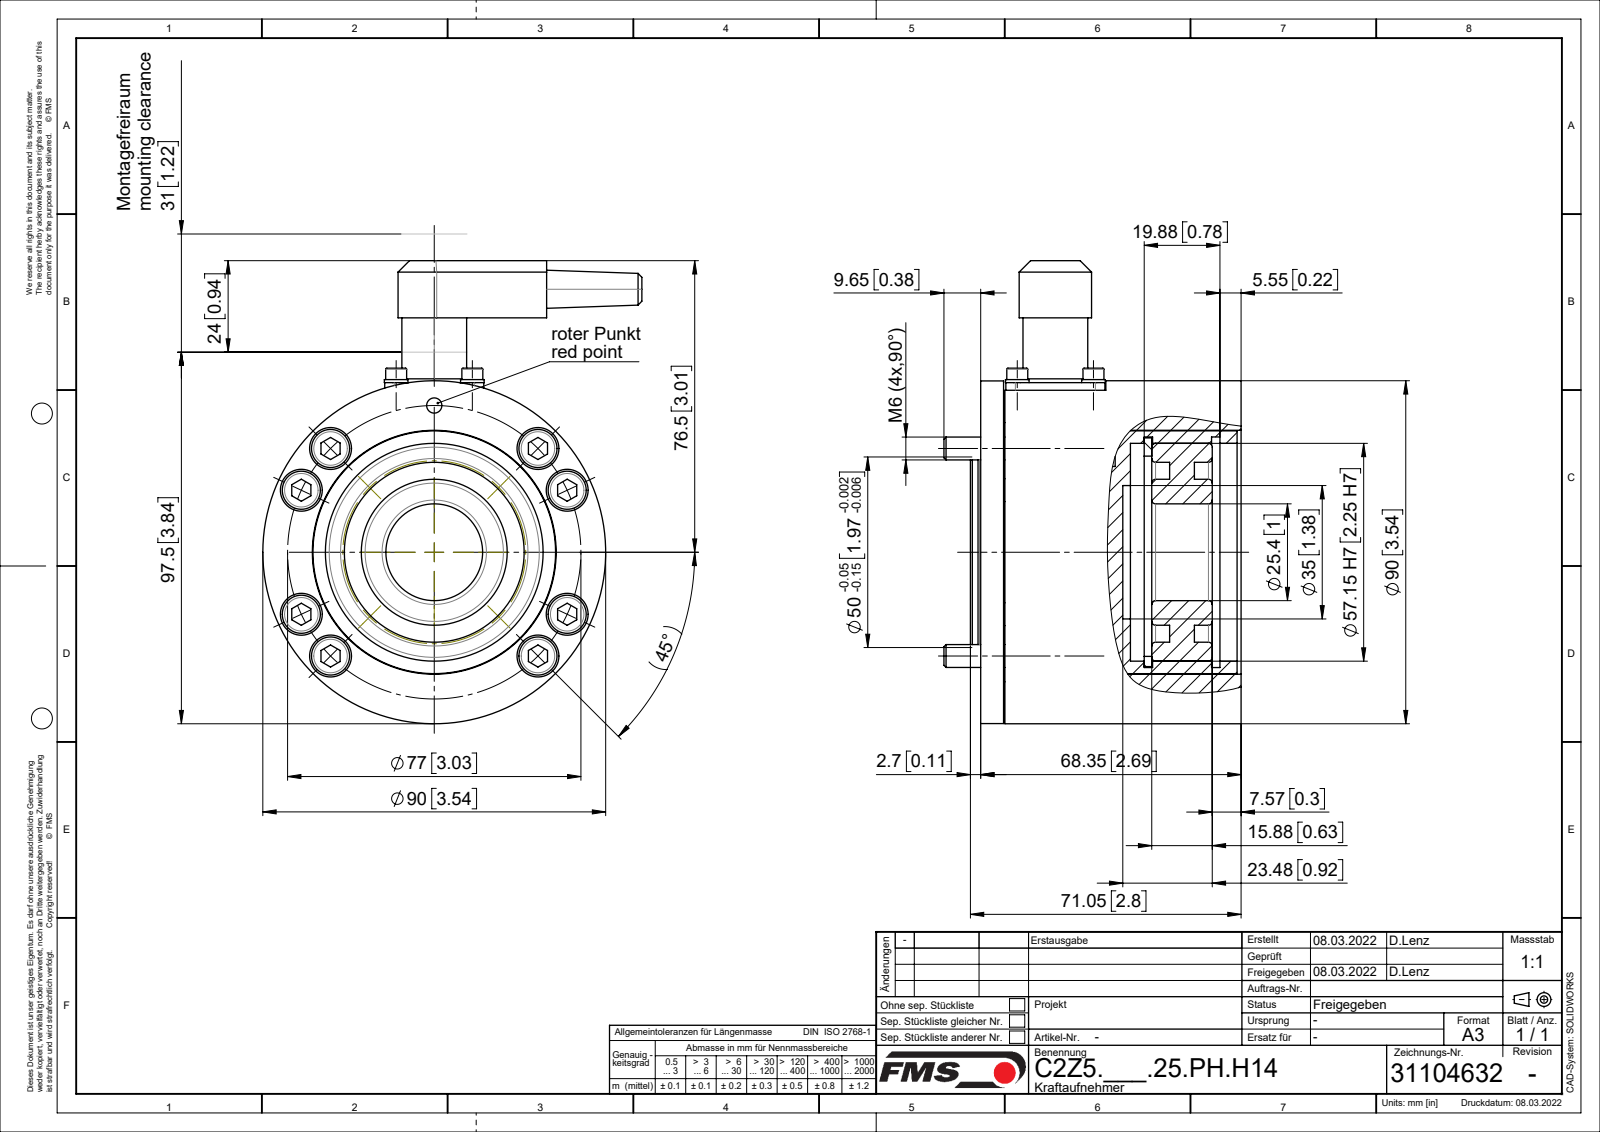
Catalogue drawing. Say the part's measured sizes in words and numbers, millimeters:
The part is named "Zyl-Schr DIN912_M6x30; 31100948_01; 31104496_stp_01; 31104488_01 (+8 more)". Its 3-D file was written by "SolidWorks 2018 (CONFIG_CONTROL_DESIGN)". It is 23 solids with 596 faces: 214 planar, 265 cylindrical and 117 other. Overall it measures 121.5 by 99.5 by 78 millimeters. Its volume is 307 740 cubic millimeters and its surface area 123 088 square millimeters. Round holes: 8 of diameter 6.5, 8 of diameter 11, 6 of diameter 2.5, 5 of diameter 2, 4 of diameter 3.1, 4 of diameter 3.2, 4 of diameter 5, 4 of diameter 7, 2 of diameter 4, 1 of diameter 10.2, 1 of diameter 12, 1 of diameter 15. Round bosses or shafts: 8 of diameter 10, 8 of diameter 6, 5 of diameter 1.5, 4 of diameter 6.2, 4 of diameter 5.5, 4 of diameter 3, 1 of diameter 90, 1 of diameter 89.9. Partial cylindrical surfaces (rounded edges, fillets, slot ends): 4 of radius 0.1, 4 of radius 2.5, 2 of radius 4.16, 2 of radius 5, 1 of radius 9.5, 1 of radius 23.2, 1 of radius 26.29. The main face-to-face distances are 6, 3.3, 2.7, 32, 33.05, 38, 2, 30, 29.3, 35.3. The hole center spacings are 20, 38.5, 13.37, 14.14, 38.49, 44.16, 54.44, 63.07.
